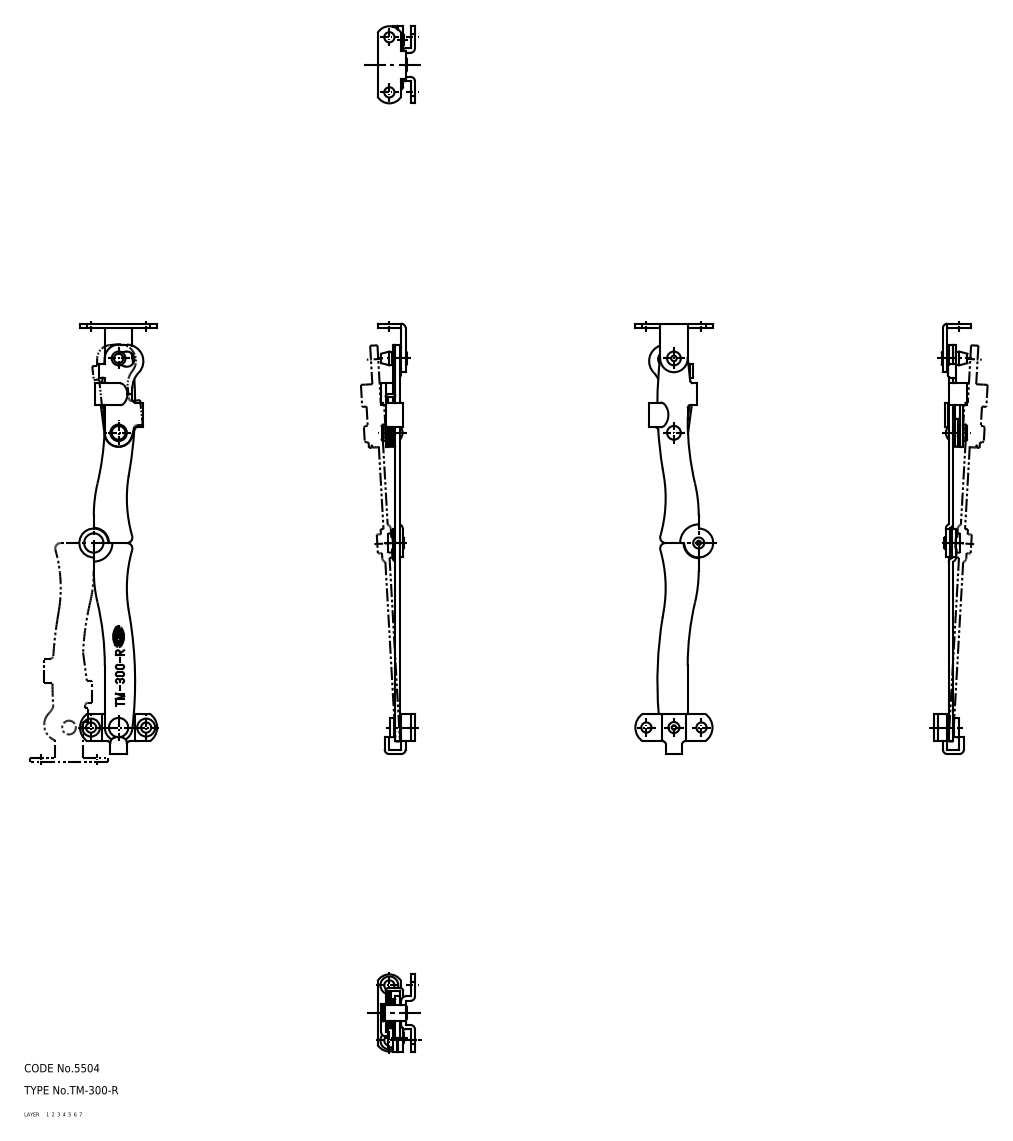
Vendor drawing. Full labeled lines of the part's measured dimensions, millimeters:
Part name (STEP PRODUCT): 67124363; 67124376; 67124389; 67124402 (+6 more)
STEP written by: CADfix (AUTOMOTIVE_DESIGN)
Units: millimetres
Bodies: 10 solids, 251 faces (0 planar, 0 cylindrical, 251 other)
Overall size (bounding box): 156.2 × 28.25 × 13.6
Volume: 5 150 mm³ · Surface area: 8 355 mm²
